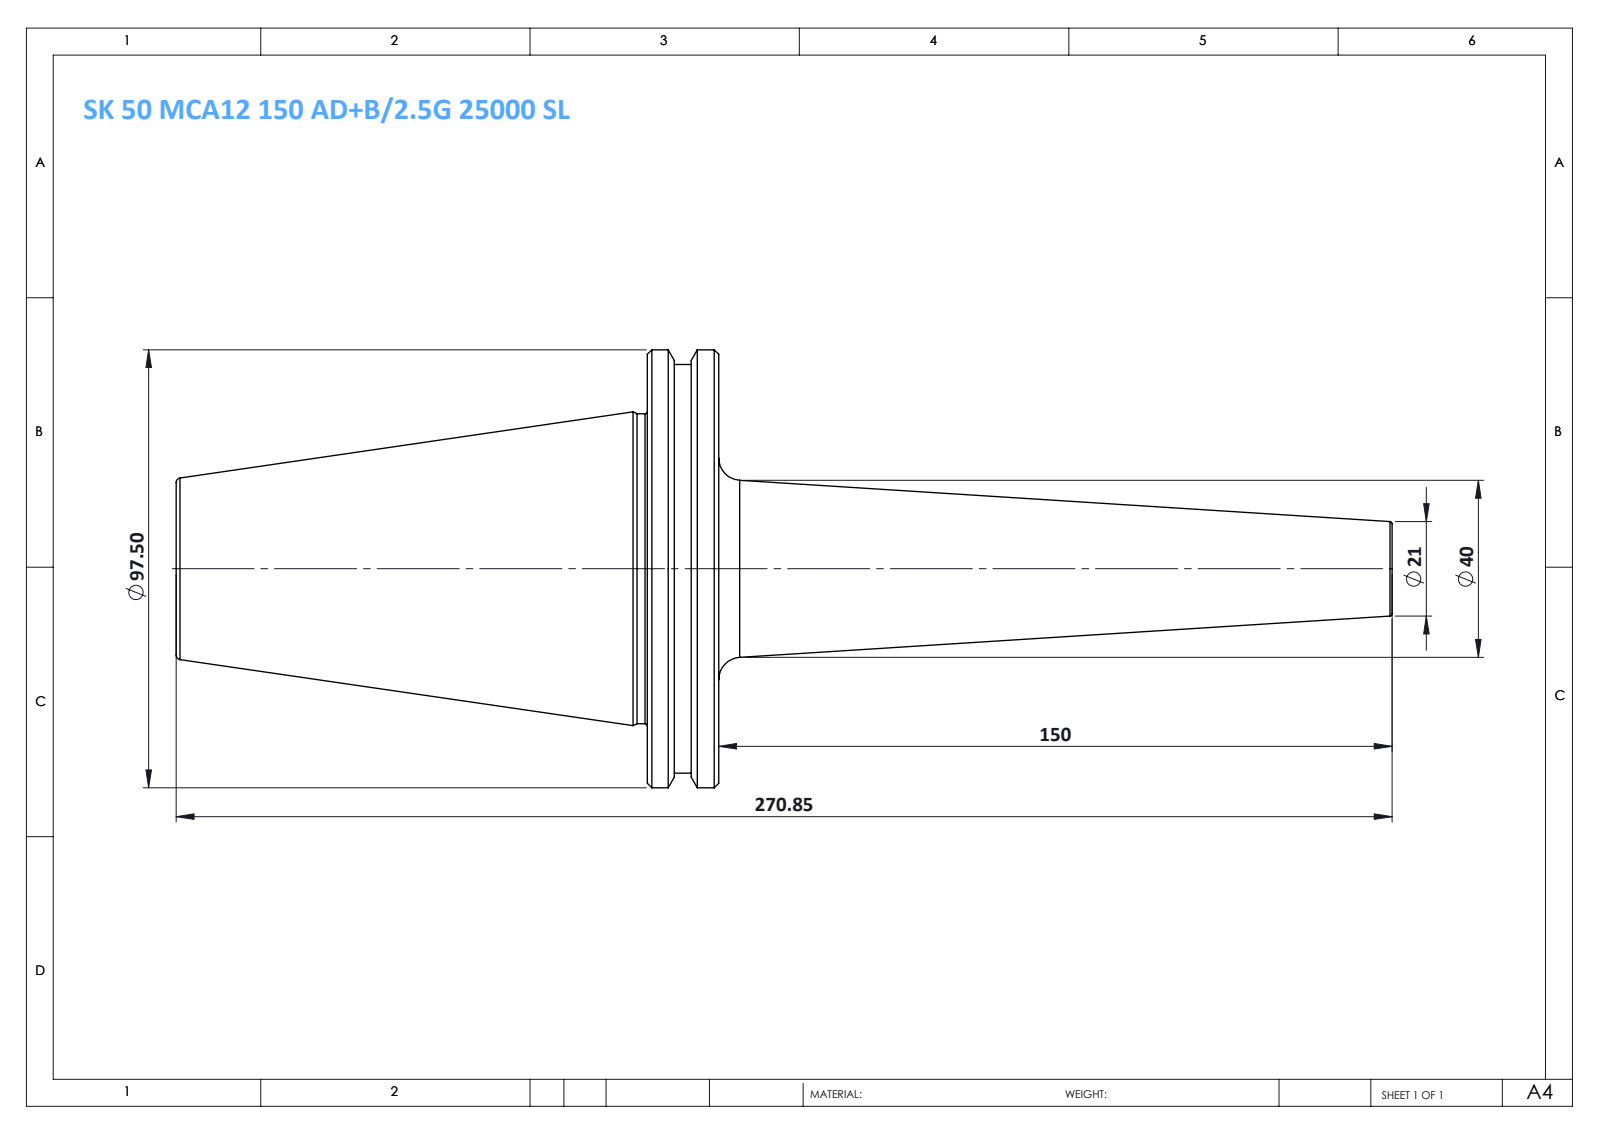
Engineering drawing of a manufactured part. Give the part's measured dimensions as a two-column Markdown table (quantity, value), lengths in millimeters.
| quantity | value |
| --- | --- |
| part name | SK 50 MCA12 150 AD+B-2.5G25000 SL |
| STEP written by | SolidWorks 2014 (CONFIG_CONTROL_DESIGN) |
| units | millimeters |
| bodies | 1 solid, 36 faces (6 planar, 8 cylindrical, 22 other) |
| overall size | 270.85 × 97.5 × 97.5 |
| volume | 487 289 mm³ |
| surface area | 49 858 mm² |
| round bosses / shafts (diameter × count) | 97.5 × 1, 91 × 1, 69 × 1 |
| main face-to-face distances | 15.9, 120.85, 104.95, 150, 165.9, 270.85, 156.13, 6.13, 9.77, 114.72 |
